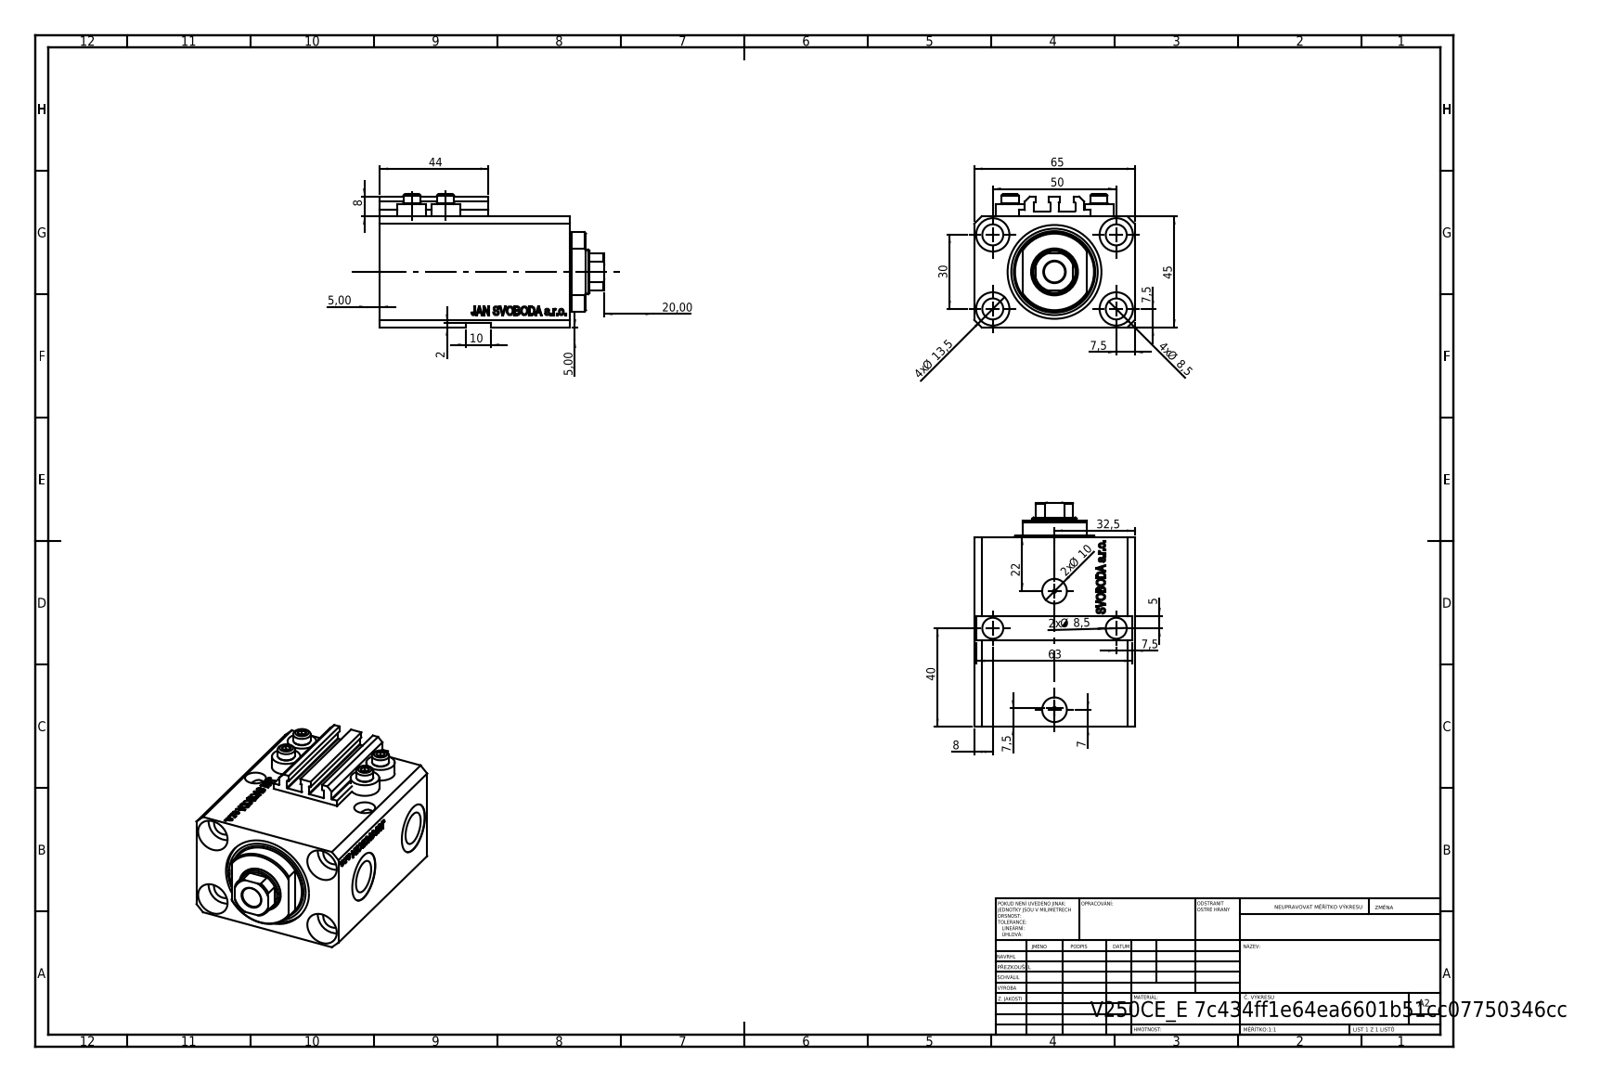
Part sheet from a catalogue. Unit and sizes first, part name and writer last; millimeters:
Units: millimetres
Overall size (bounding box): 90.9 × 65 × 54
Round holes (diameter × count): ⌀8.5 ×7, ⌀1.25 ×4, ⌀4 ×4, ⌀13.5 ×4, ⌀10 ×2, ⌀13.16 ×2, ⌀20 ×2, ⌀18 ×1, ⌀25 ×1, ⌀38 ×1
Round bosses / shafts (diameter × count): ⌀11.6 ×4, ⌀7 ×4
Partial cylindrical surfaces — rounded edges, fillets, slot ends (radius × count): R0.2 ×10, R8.5 ×1, R16 ×1
Main face-to-face distances: 45, 65, 51.9, 77, 25.1, 2, 6.9, 70.1, 3, 9
Hole centre spacings: 29.15, 50, 13.6, 15.12, 18.81, 18.97, 26.22, 26.61
Volume: 199 765 mm³ · Surface area: 61 291 mm²
Bodies: 8 solids, 1067 faces (511 planar, 126 cylindrical, 430 other)
Part name (STEP PRODUCT): V250CE_E_Body; ALLEN BOLT V250CE; V250CE_VC_E; V250CE_C_VCP
STEP written by: SolidWorks 2019 (CONFIG_CONTROL_DESIGN)
